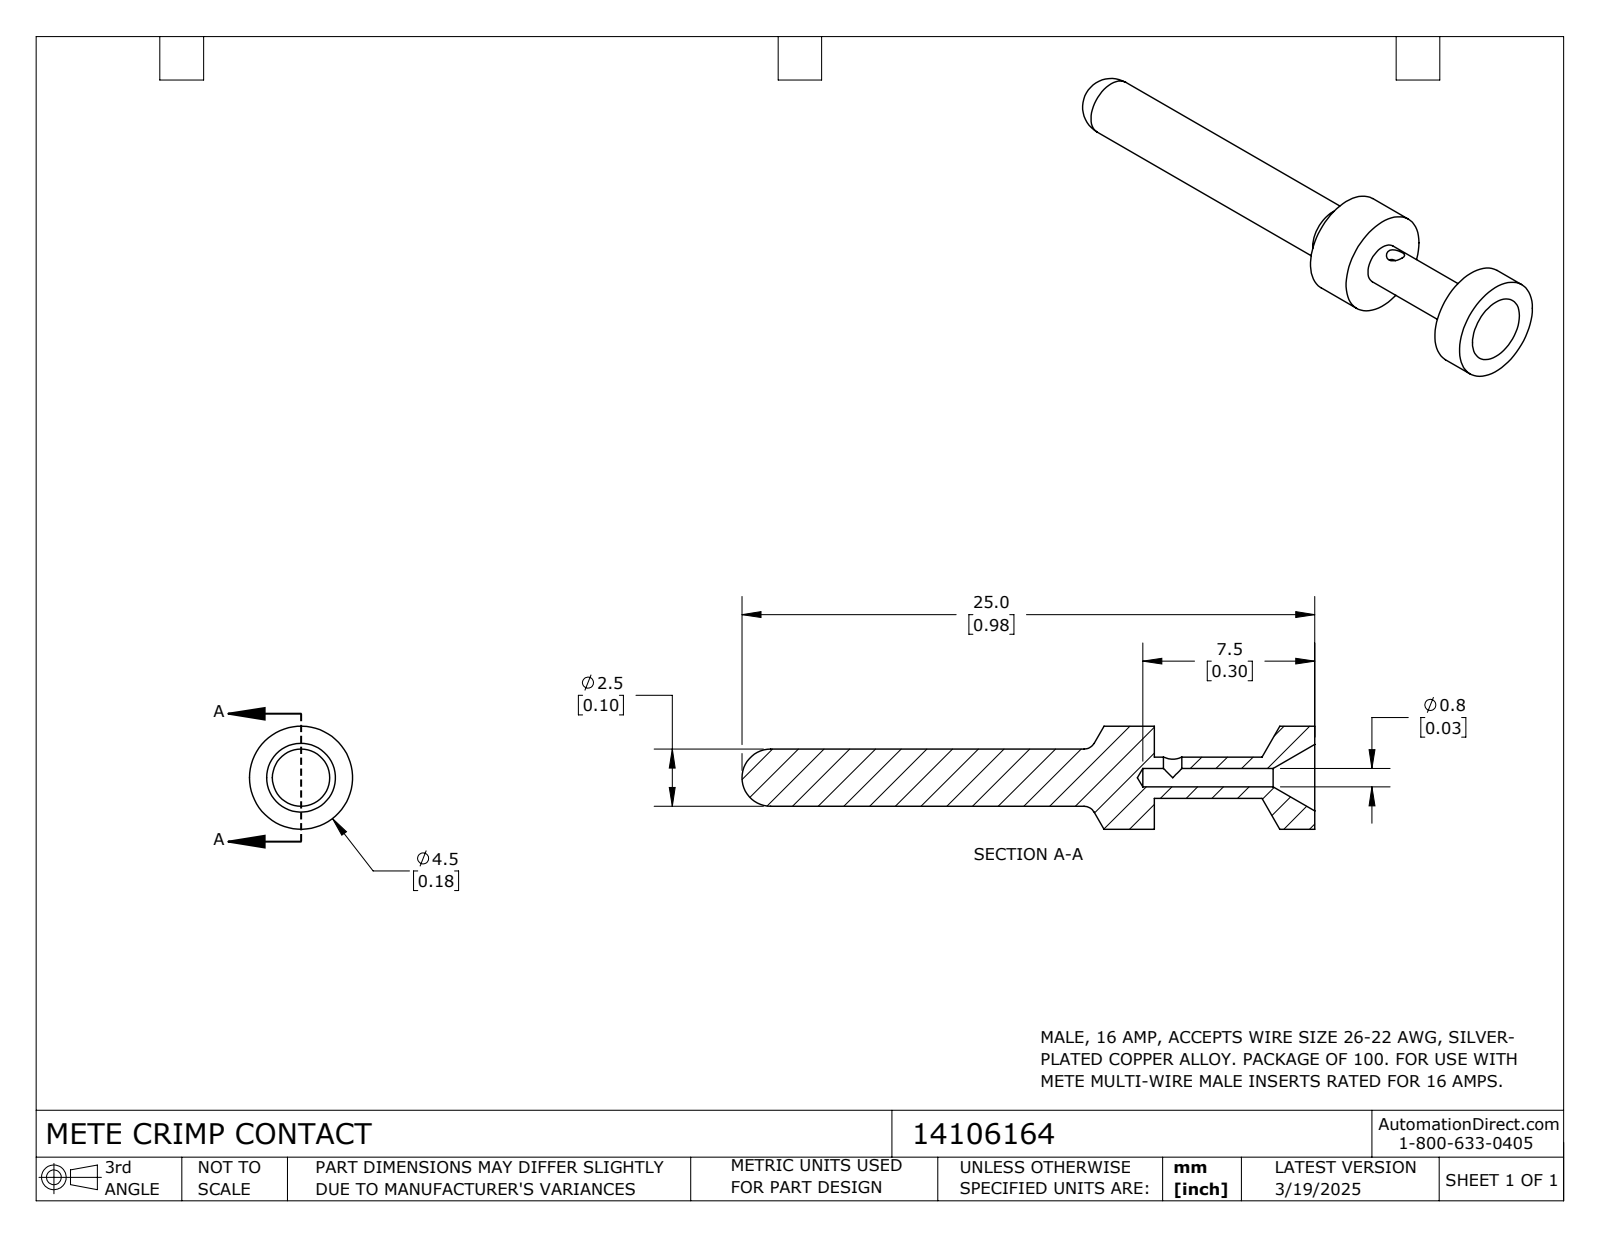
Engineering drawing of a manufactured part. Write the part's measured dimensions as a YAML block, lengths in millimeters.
part_name: "14106164"
step_written_by: "SolidWorks 2024 (CONFIG_CONTROL_DESIGN)"
units: millimeters
bodies: {solids: 1, faces: 27, planar: 2, cylindrical: 13, other: 12}
overall_size: [25, 4.5, 4.5]
volume: 147
surface_area: 277
round_holes:
  - {diameter: 0.8, count: 2}
round_bosses_or_shafts:
  - {diameter: 4.5, count: 1}
  - {diameter: 2.5, count: 1}
  - {diameter: 1.8, count: 1}
face_to_face_distances: [7]
